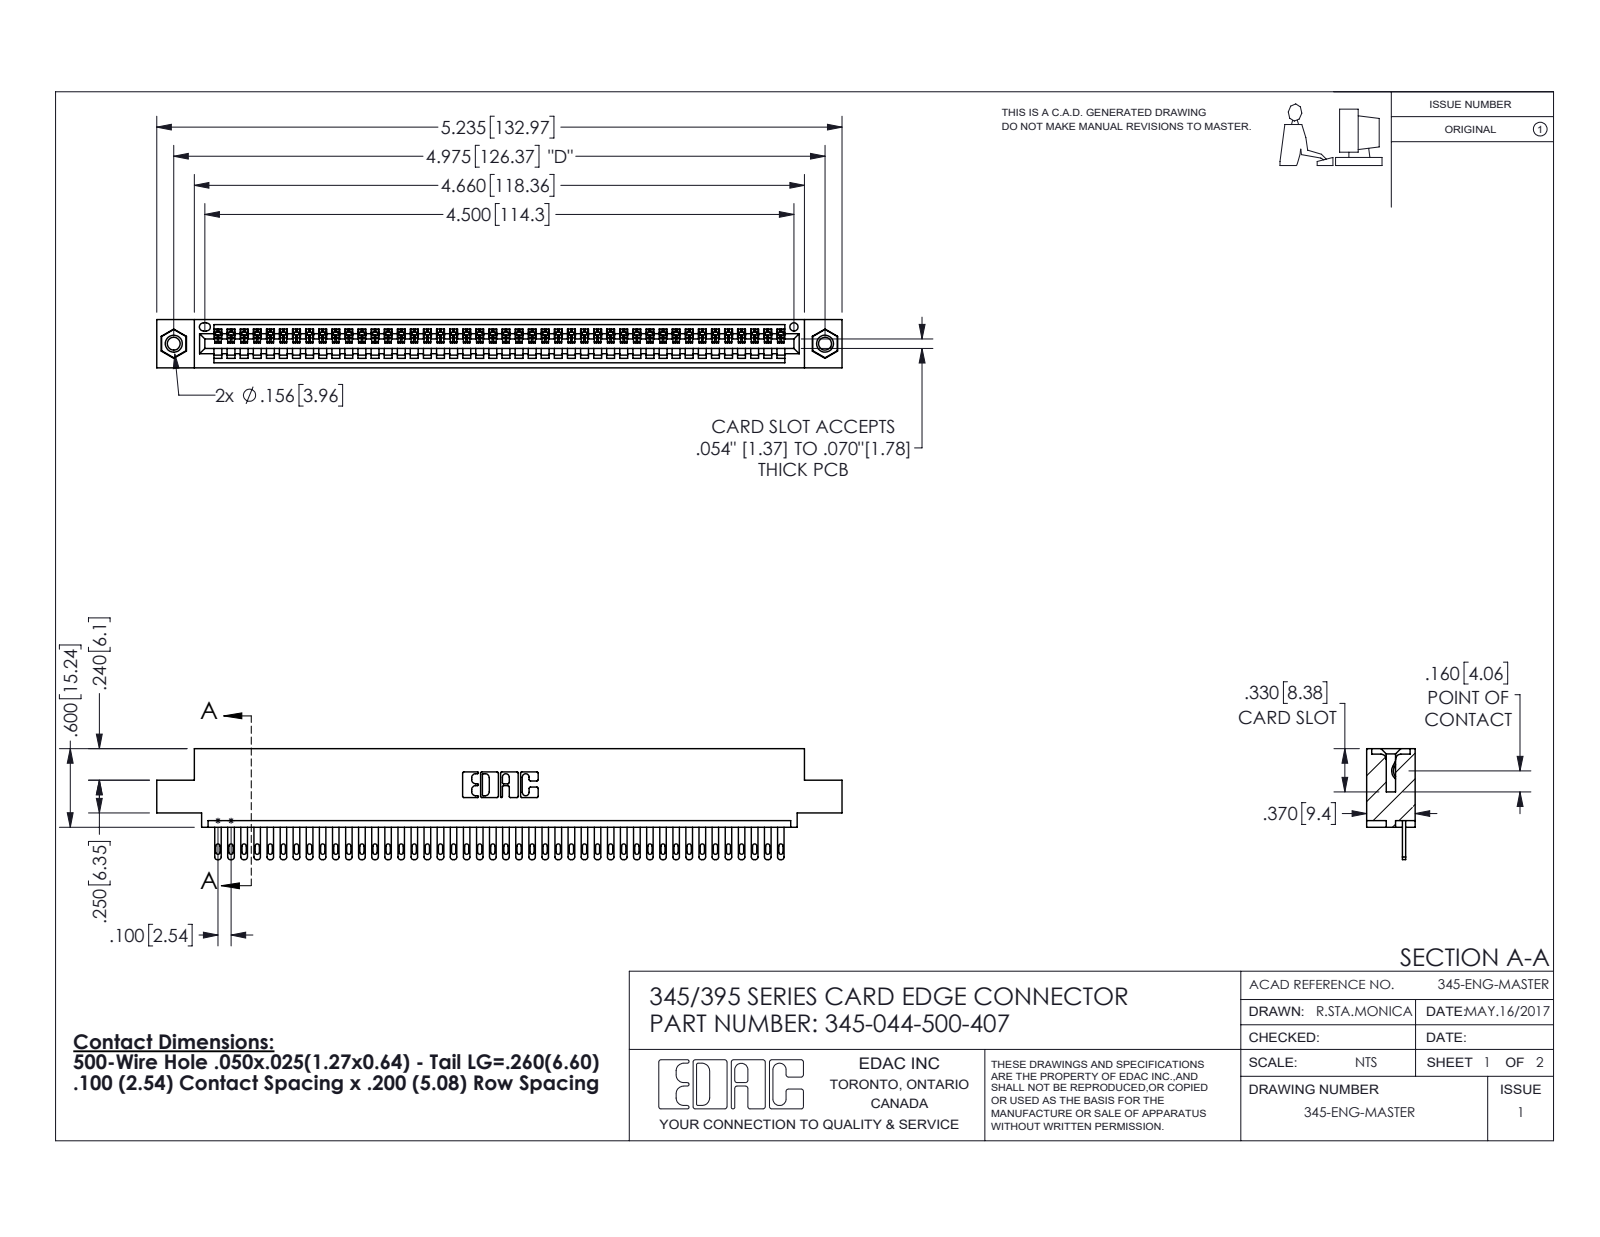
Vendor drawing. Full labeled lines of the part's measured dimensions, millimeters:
Part name (STEP PRODUCT): 345-044-500-407; 345-292-001_345-293-100; 345 Part_0.110 Offset - 0.156 Dia-TI; 345-250-001_345-250-005-103
STEP written by: SolidWorks 2016 (CONFIG_CONTROL_DESIGN)
Units: millimetres
Bodies: 47 solids, 2566 faces (1612 planar, 938 cylindrical, 16 other)
Overall size (bounding box): 133 × 21.5 × 9.4
Volume: 12 600 mm³ · Surface area: 16 970 mm²
Round holes (diameter × count): ⌀2.5 ×2, ⌀3.2 ×2, ⌀4 ×2, ⌀1.6 ×1
Round bosses / shafts (diameter × count): ⌀3.9 ×2
Partial cylindrical surfaces — rounded edges, fillets, slot ends (radius × count): R0.2 ×88, R0.4 ×88, R0.5 ×88, R0.3 ×22, R0.2 ×6, R0.8 ×6, R0.7 ×3, R0.8 ×2
Main face-to-face distances: 1.8, 7.6, 9.4, 2.5, 6.9, 0.6, 5.1, 5.7, 3.8, 1.8
Hole centre spacings: 6.9, 120.4, 126.4
